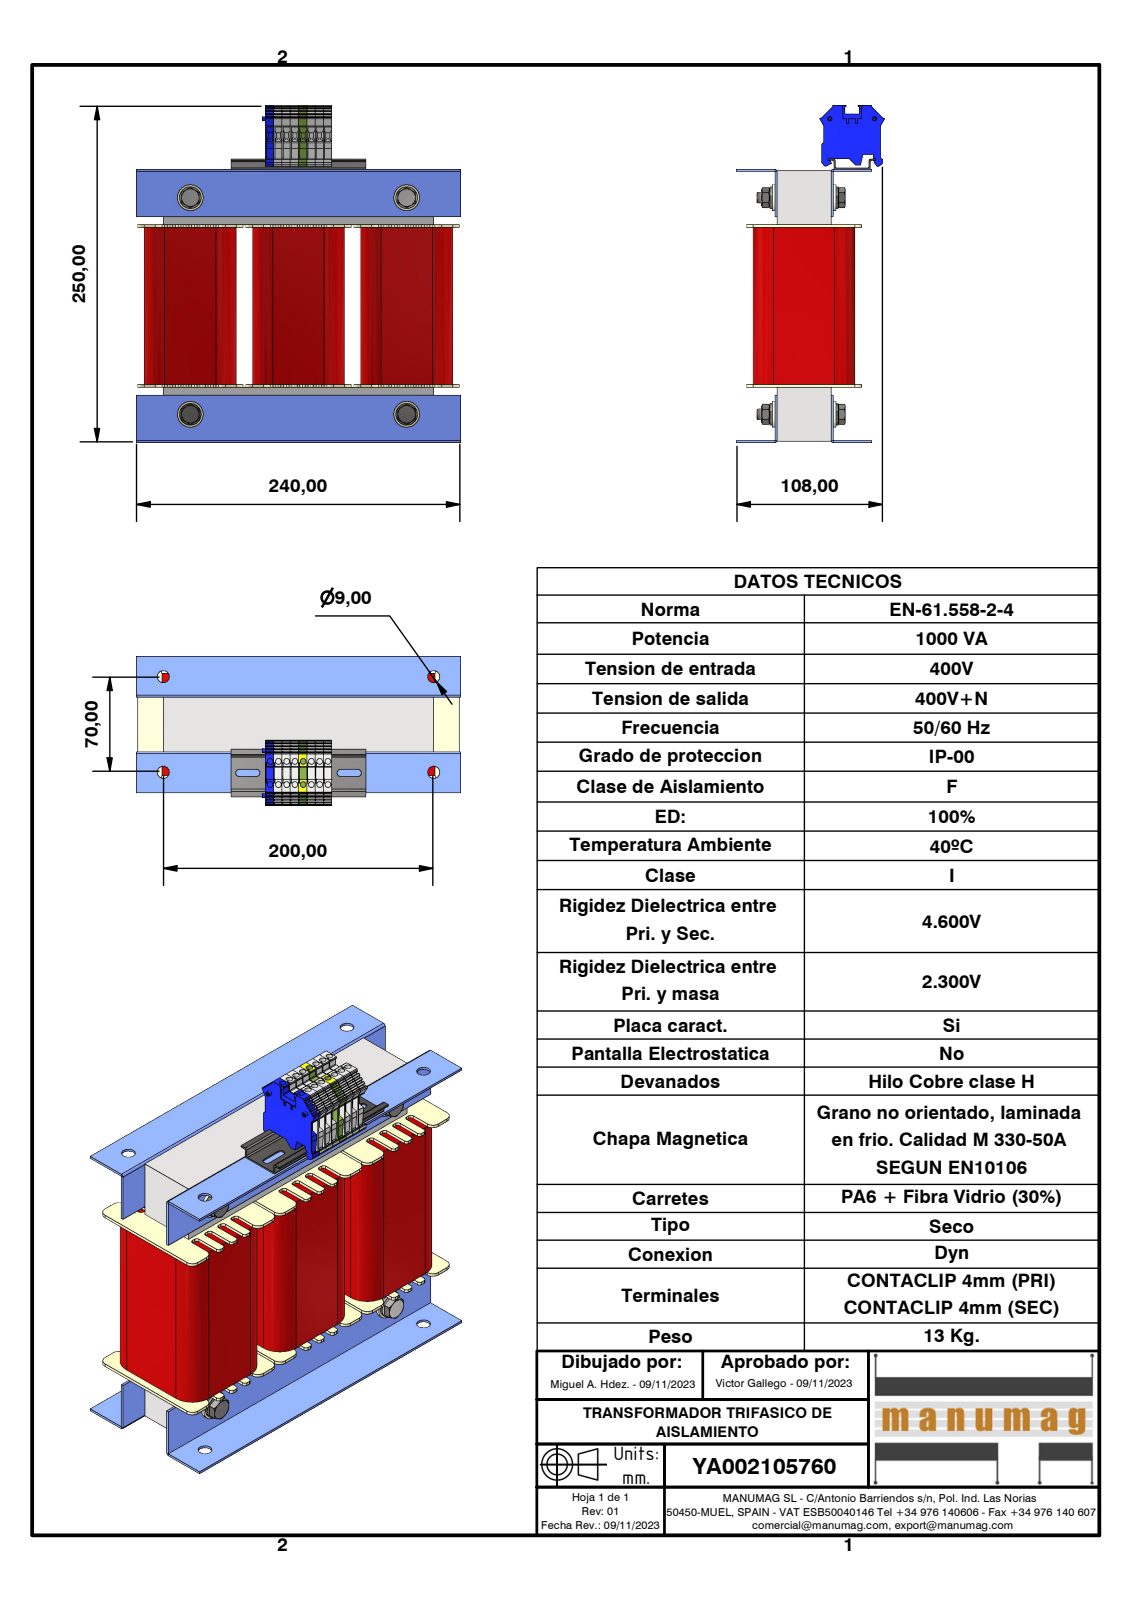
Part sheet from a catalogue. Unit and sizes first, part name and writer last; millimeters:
Units: millimetres
Overall size (bounding box): 249.25 × 240 × 109.53
Round holes (diameter × count): ⌀4.3 ×16, ⌀6.65 ×4, ⌀8 ×4, ⌀8.4 ×4, ⌀9 ×4, ⌀10.5 ×4, ⌀11 ×4, ⌀2.4 ×2, ⌀2.5 ×2, ⌀2.75 ×2, ⌀2.95 ×2
Round bosses / shafts (diameter × count): ⌀19 ×4, ⌀16 ×4, ⌀11.4 ×4, ⌀9.6 ×4, ⌀7.32 ×4
Partial cylindrical surfaces — rounded edges, fillets, slot ends (radius × count): R2 ×85, R5 ×24, R0.25 ×16, R1 ×12, R15 ×12, R2.6 ×8, R0.3 ×5, R0.5 ×5
Main face-to-face distances: 40, 1.5, 80, 160, 41.5, 120, 14, 54, 43, 161
Hole centre spacings: 6.1, 18.06, 12.2, 20.92, 18.3, 24.98, 17, 24.4
Volume: 2 590 000 mm³ · Surface area: 513 215 mm²
Bodies: 41 solids, 2938 faces (2090 planar, 680 cylindrical, 168 other)
Part name (STEP PRODUCT): YA002105760; 3UI120 200 x 200 - 40 (Rc40); UI 120_40; RC40 NT040 (+8 more)
STEP written by: Autodesk Inventor 2023 (AUTOMOTIVE_DESIGN)
